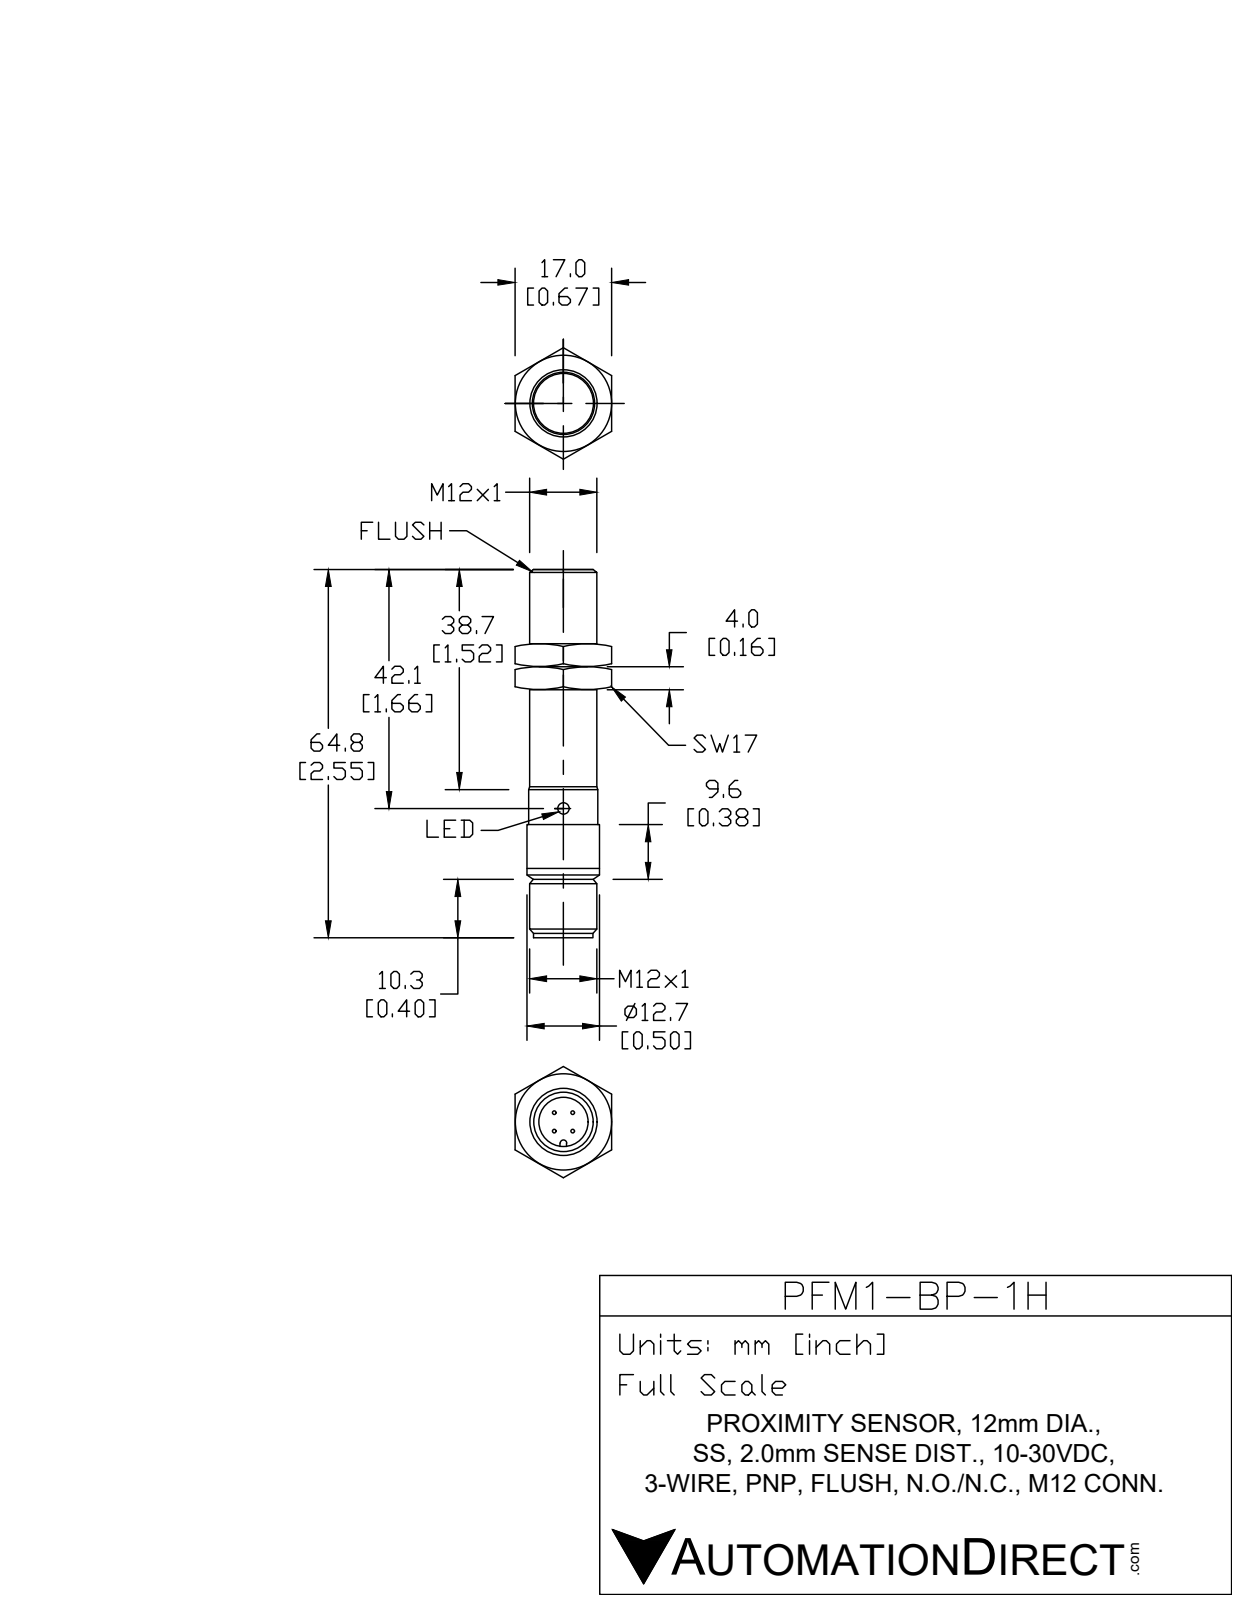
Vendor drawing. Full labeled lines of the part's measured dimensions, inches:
Part name (STEP PRODUCT): PFM1-BP-1H
STEP written by: SolidWorks 2017 (AUTOMOTIVE_DESIGN)
Units: inches
Bodies: 3 solids, 70 faces (10 planar, 36 cylindrical, 24 other)
Overall size (bounding box): 2.543 × 0.5 × 0.5
Volume: 0.422 in³ · Surface area: 6.12 in²
Round holes (diameter × count): ⌀0.118 ×1, ⌀0.331 ×1, ⌀0.335 ×1, ⌀0.374 ×1
Round bosses / shafts (diameter × count): ⌀0.039 ×4, ⌀0.5 ×1, ⌀0.472 ×1, ⌀0.413 ×1, ⌀0.396 ×1, ⌀0.37 ×1
Partial cylindrical surfaces — rounded edges, fillets, slot ends (radius × count): R0.024 ×1, R0.219 ×1
Main face-to-face distances: 0.071, 2.075, 2.146, 2.193, 0.118, 0.047, 2.504, 0.429, 0.358, 0.311
